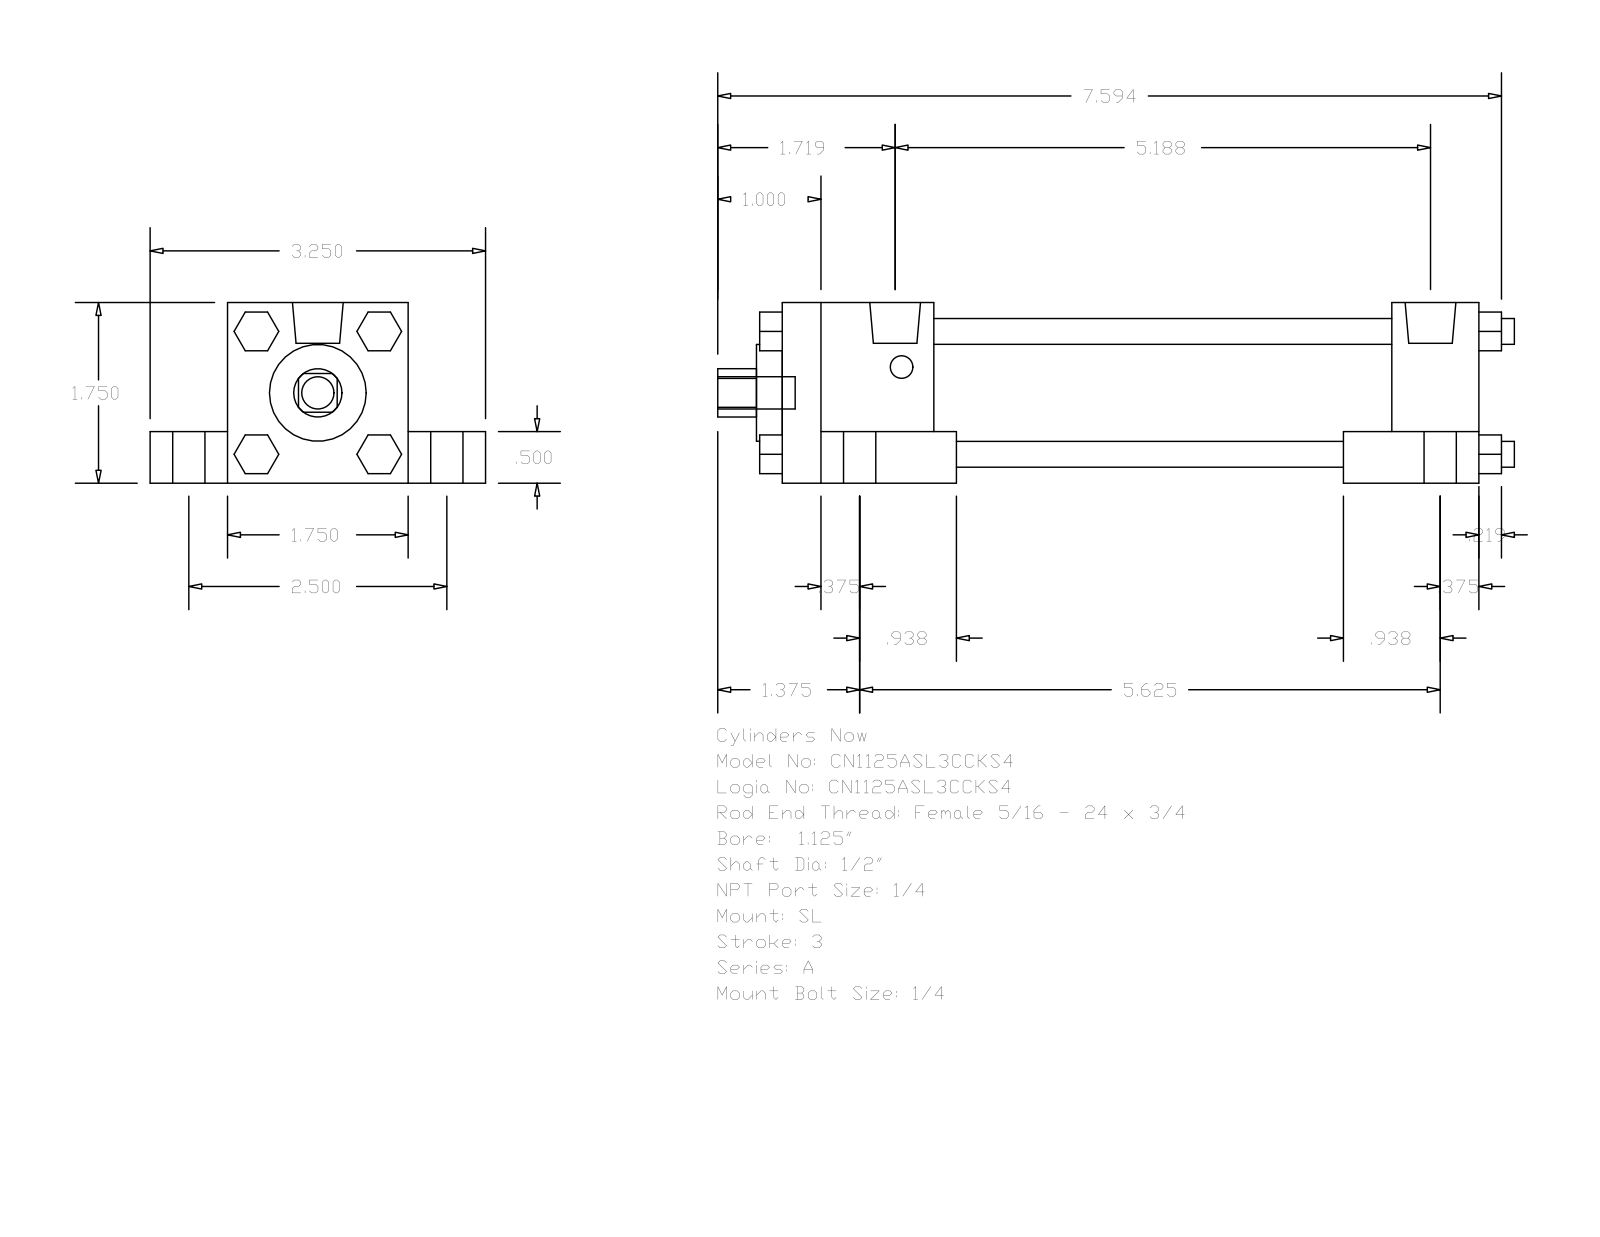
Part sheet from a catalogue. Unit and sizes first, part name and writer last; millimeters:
Units: millimetres
Overall size (bounding box): 196.06 × 82.55 × 44.45
Round holes (diameter × count): ⌀12.7 ×1, ⌀23.81 ×1, ⌀31.88 ×1
Round bosses / shafts (diameter × count): ⌀7.94 ×5, ⌀14.29 ×4, ⌀6.35 ×4, ⌀5.56 ×4, ⌀12.49 ×2
Partial cylindrical surfaces — rounded edges, fillets, slot ends (radius × count): R5.94 ×1
Main face-to-face distances: 44.46, 31.76, 12.7, 19.04, 63.5, 134.14, 171.44, 150.01, 21.43, 37.3
Bodies: 0 solids, 150 faces (114 planar, 36 cylindrical, 0 other)
Part name (STEP PRODUCT): A_SL__0112_0.5
STEP written by: GSSL Pune (CONFIG_CONTROL_DESIGN)
